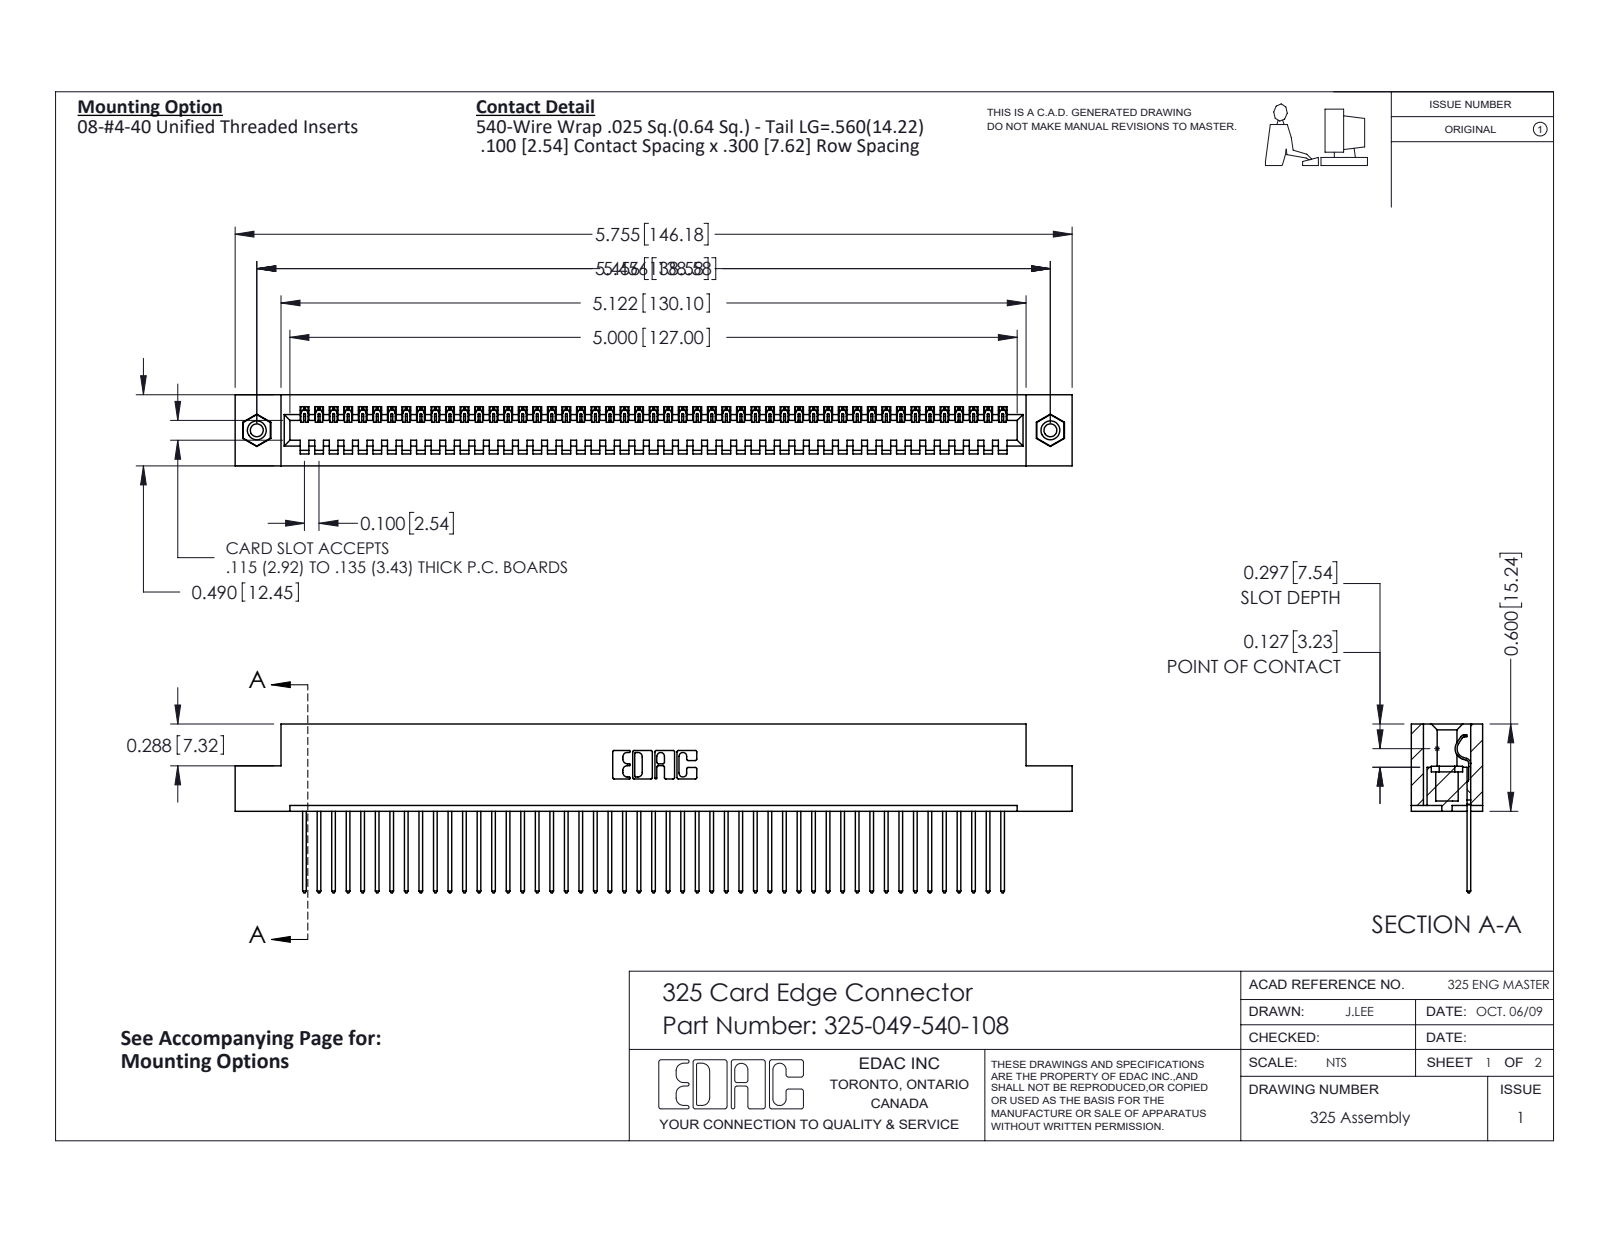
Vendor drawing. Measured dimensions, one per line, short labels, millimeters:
name: 325-049-540-108; 345-250-001_345-250-003-102; 325-292-001_325-293-140; 325 Part_TI
written by: SolidWorks 2016 (CONFIG_CONTROL_DESIGN)
unit: mm
bodies: 52 solids, 3016 faces (2160 planar, 840 cylindrical, 16 other)
size: 146.2 × 29.5 × 12.4
volume: 18 660 mm³; area: 21 030 mm²
holes: 2× ⌀2.3, 2× ⌀3.2, 2× ⌀4.1
bosses: 2× ⌀3.9
rounds: 98× R0.2, 98× R0.3, 22× R0.3, 6× R0.2, 6× R0.8, 3× R0.7, 1× R0.4, 1× R0.6
face distances: 2.1, 10.3, 12.4, 7.6, 2.7, 9.7, 0.6, 8.3, 14.2, 6.7
hole spacings: 138.6
